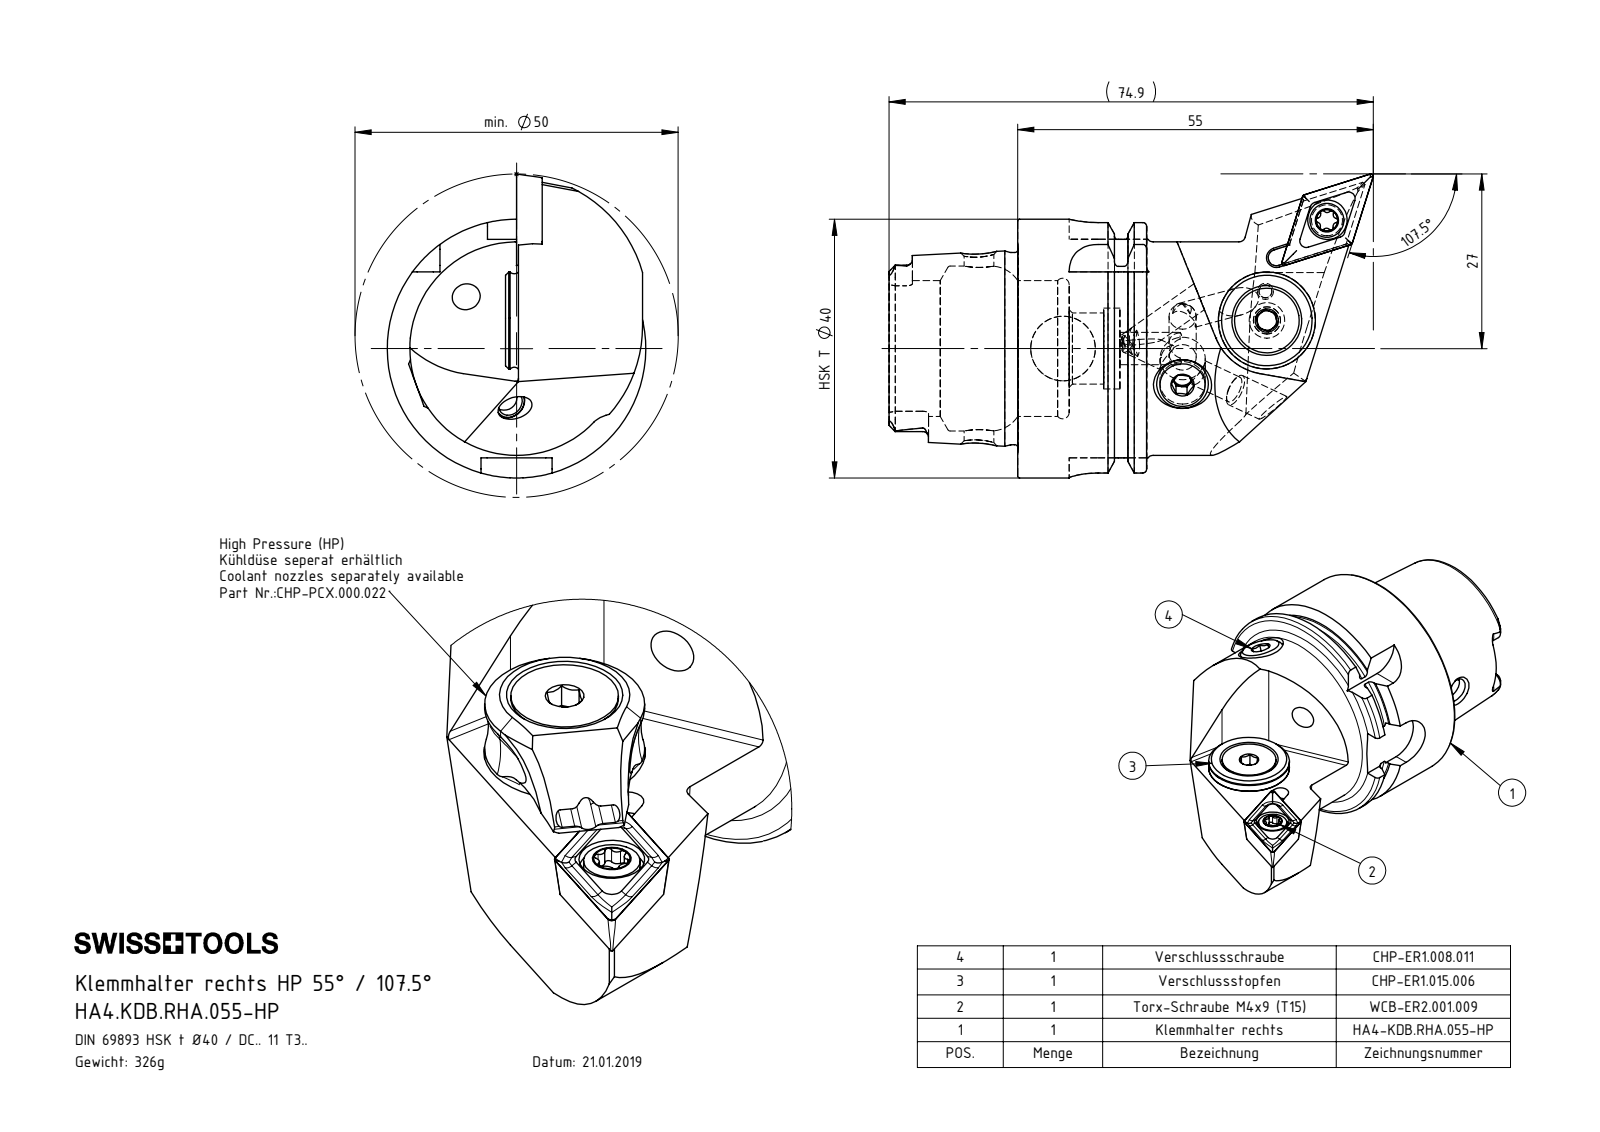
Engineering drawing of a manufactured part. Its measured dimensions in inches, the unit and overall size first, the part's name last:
Units: inches
Overall size (bounding box): 2.949 × 1.85 × 1.575
Round holes (diameter × count): ⌀0.165 ×5, ⌀0.197 ×2, ⌀0.047 ×1, ⌀0.079 ×1, ⌀0.098 ×1, ⌀0.118 ×1, ⌀0.13 ×1, ⌀0.157 ×1, ⌀0.173 ×1, ⌀0.181 ×1, ⌀0.205 ×1, ⌀0.24 ×1
Round bosses / shafts (diameter × count): ⌀0.197 ×2, ⌀1.575 ×1, ⌀1.368 ×1, ⌀1.299 ×1, ⌀1.17 ×1, ⌀0.591 ×1, ⌀0.528 ×1, ⌀0.394 ×1
Partial cylindrical surfaces — rounded edges, fillets, slot ends (radius × count): R0.013 ×6, R0.023 ×6, R0.035 ×6, R0.177 ×4, R0.02 ×2, R0.072 ×2, R0.074 ×2, R0.049 ×1
Main face-to-face distances: 0.177, 0.313, 0.472, 0.785, 0.033, 0.144, 0.783, 1.096, 1.569, 1.406
Hole centre spacings: 0.177, 0.572, 0.578, 0.711, 0.716, 1.254, 1.281, 1.787
Volume: 2.512 in³ · Surface area: 25.58 in²
Bodies: 10 solids, 474 faces (119 planar, 135 cylindrical, 220 other)
Part name (STEP PRODUCT): KD..RHA.055-HP; CHP-ER1.008.011_A; DCMT11T304; KVT_MB_600_050 (+7 more)
STEP written by: SolidWorks 2017 (AUTOMOTIVE_DESIGN)
